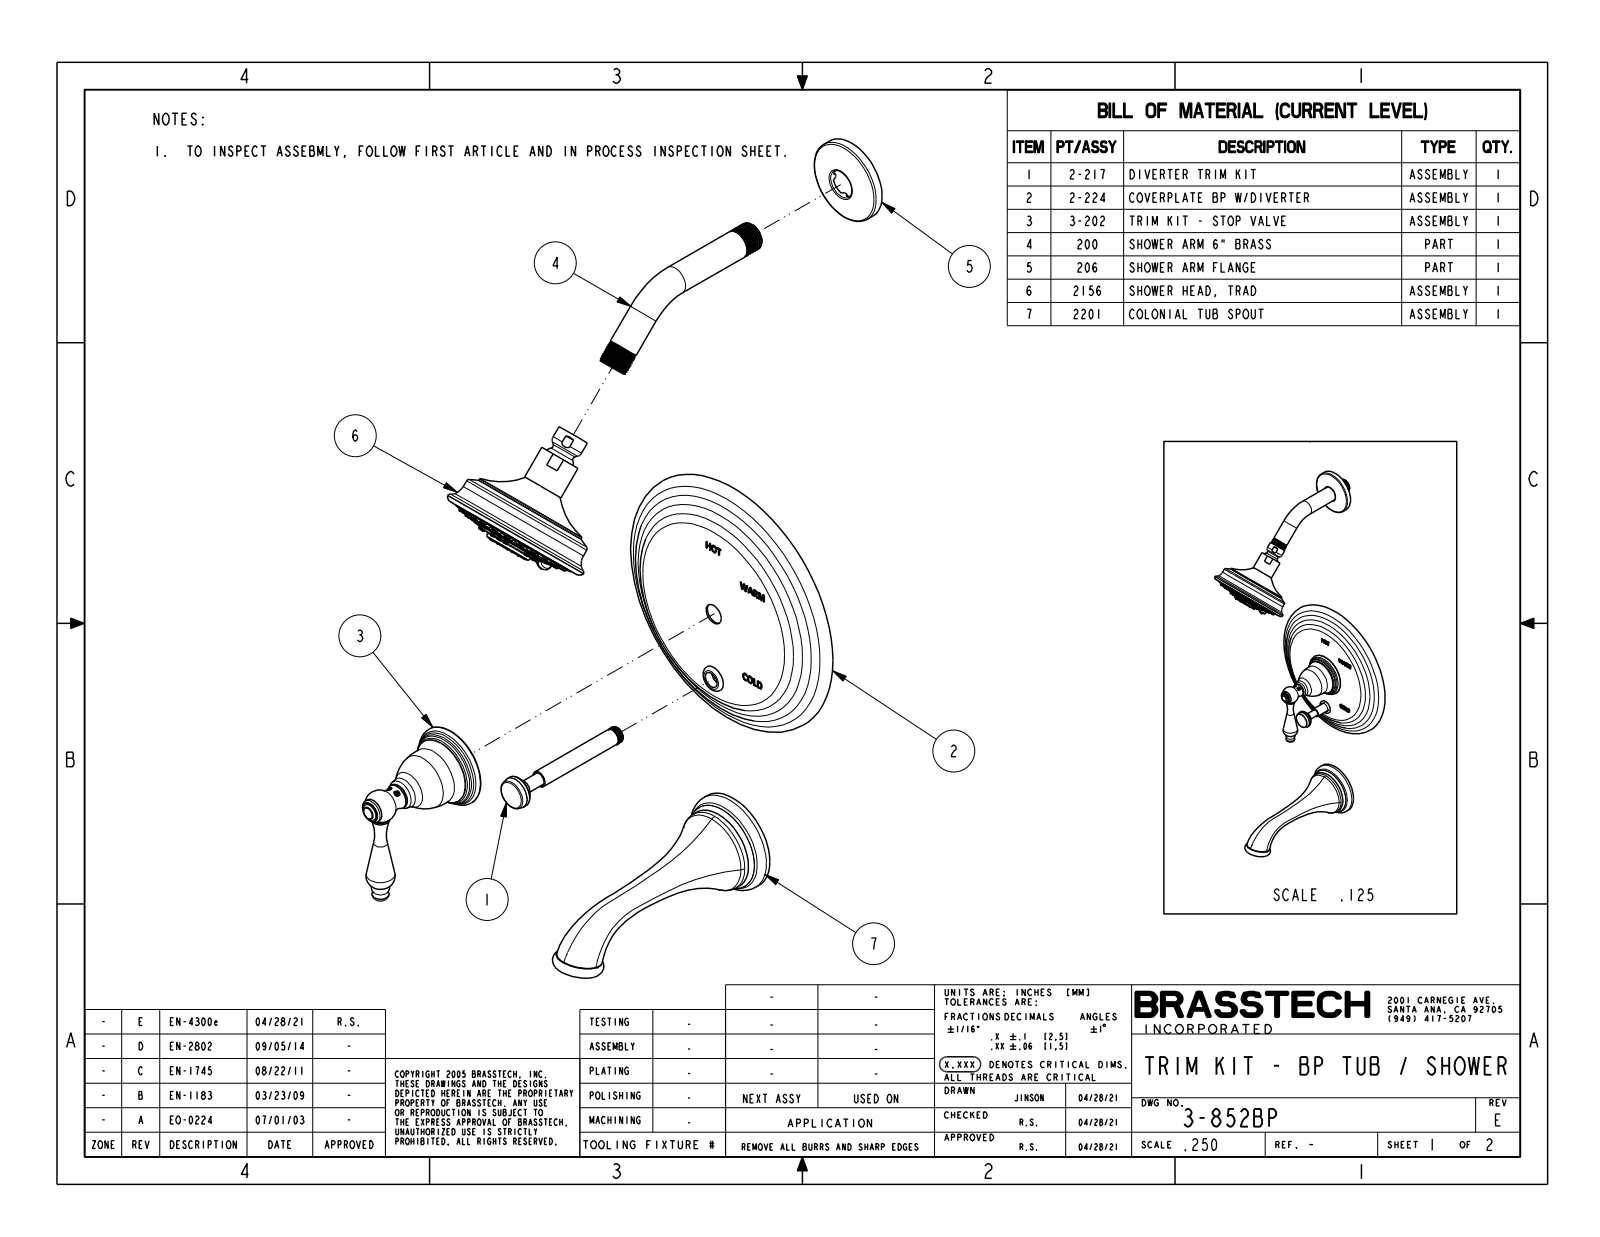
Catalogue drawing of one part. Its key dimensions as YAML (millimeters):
part_name: "3-852BP"
step_written_by: "CREO PARAMETRIC BY PTC INC, 2018400 (CONFIG_CONTROL_DESIGN)"
units: millimeters
bodies: {solids: 3, faces: 1343, planar: 244, cylindrical: 218, other: 881}
overall_size: [574.5, 209.6, 196.9]
volume: 1041000
surface_area: 150500
round_holes:
  - {diameter: 1.5, count: 8}
  - {diameter: 23.5, count: 1}
round_bosses_or_shafts:
  - {diameter: 3.6, count: 39}
  - {diameter: 4.2, count: 23}
  - {diameter: 20.7, count: 2}
  - {diameter: 96.8, count: 1}
  - {diameter: 94.6, count: 1}
  - {diameter: 82.3, count: 1}
  - {diameter: 72.4, count: 1}
  - {diameter: 63.7, count: 1}
partial_cylinders:
  - {radius: 2, count: 8}
  - {radius: 0.5, count: 2}
  - {radius: 3.5, count: 1}
  - {radius: 12, count: 1}
  - {radius: 13, count: 1}
  - {radius: 16, count: 1}
face_to_face_distances: [19.2, 1.6, 3, 4.6, 14.6, 4.5, 66.5, 51.9, 47.4, 7.4]
hole_center_spacings: [11.3, 14.7, 20.8, 20.8, 27.2, 11.3, 14.7, 27.2]
